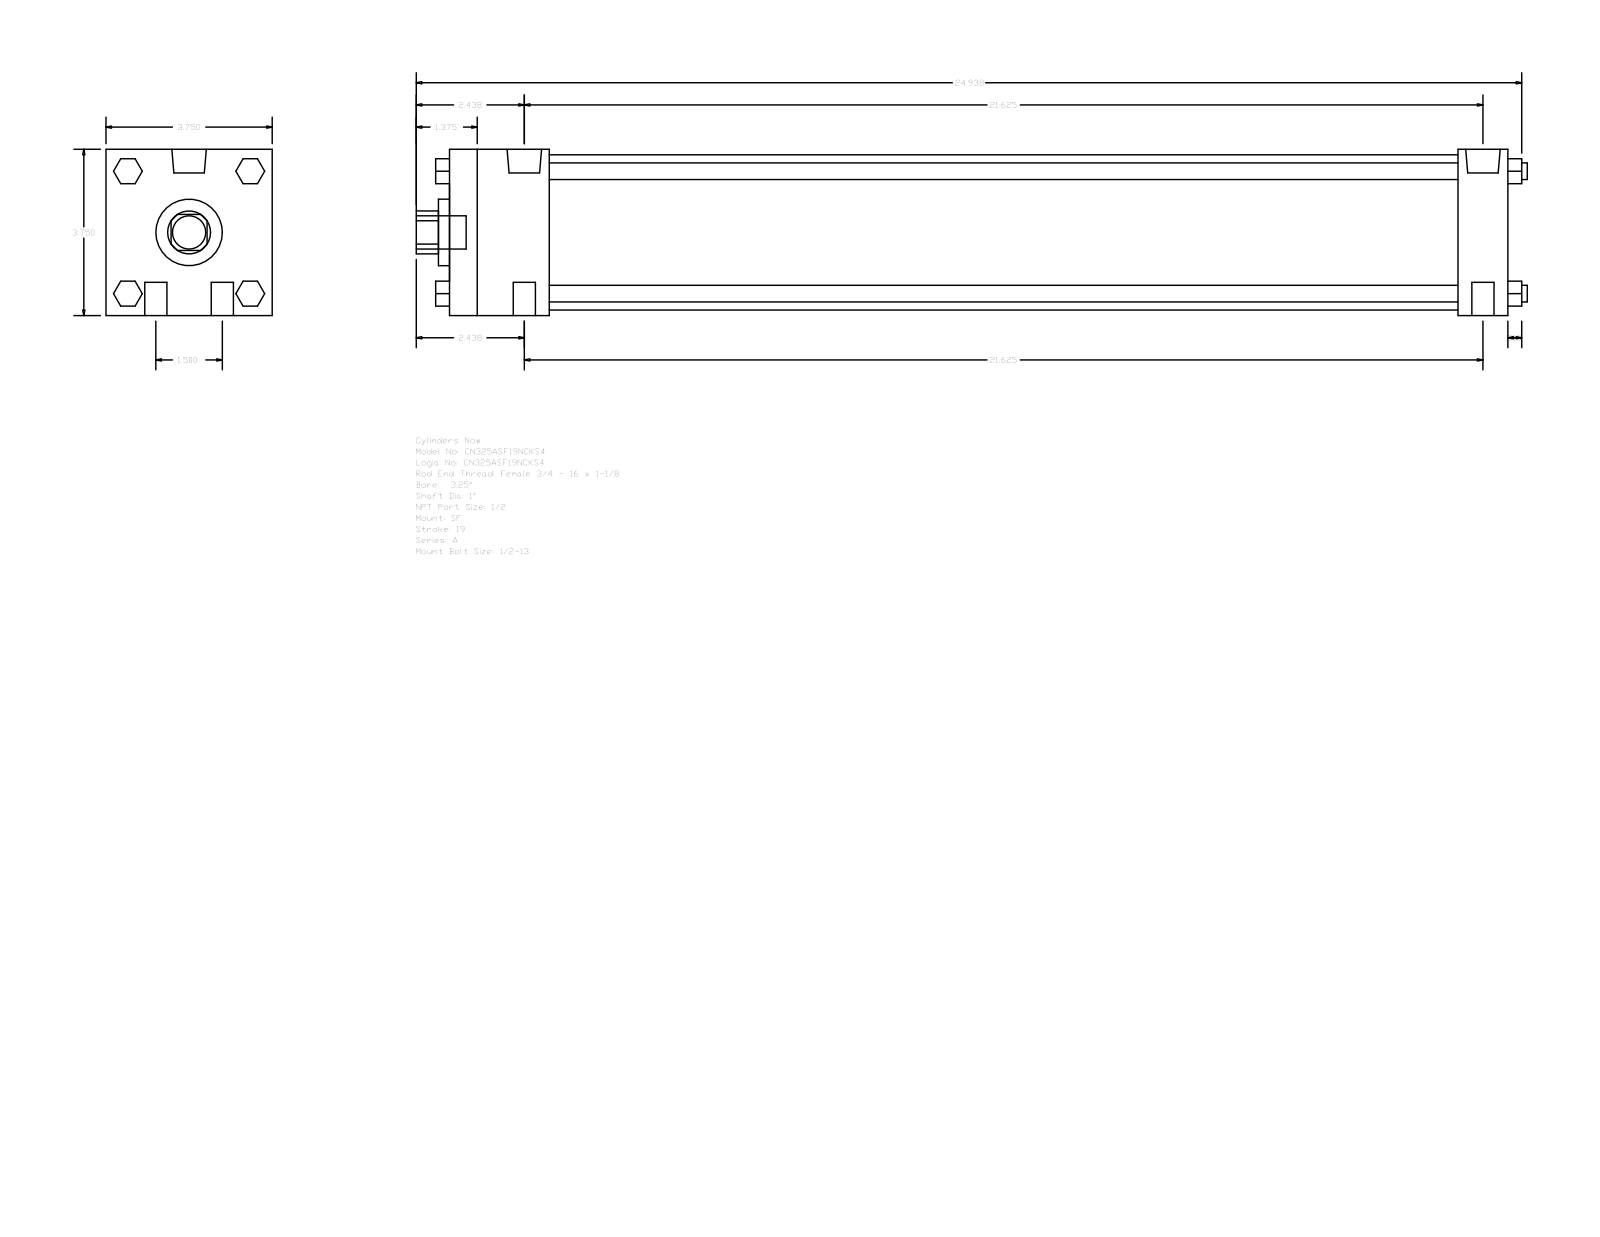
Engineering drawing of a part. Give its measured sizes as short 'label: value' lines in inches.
name: A_SF__0325_1
written by: GSSL Pune (CONFIG_CONTROL_DESIGN)
unit: in
bodies: 0 solids, 124 faces (94 planar, 30 cylindrical, 0 other)
size: 25.063 × 3.75 × 3.75
holes: 1× ⌀1, 1× ⌀1.5, 1× ⌀3.5
bosses: 4× ⌀0.5, 4× ⌀0.375, 2× ⌀0.778, 2× ⌀0.344, 1× ⌀0.75
rounds: 1× R0.484
face distances: 3.75, 23.875, 22.75, 1.125, 2.25, 20.5, 21.625, 0.562, 1.38, 2.39
